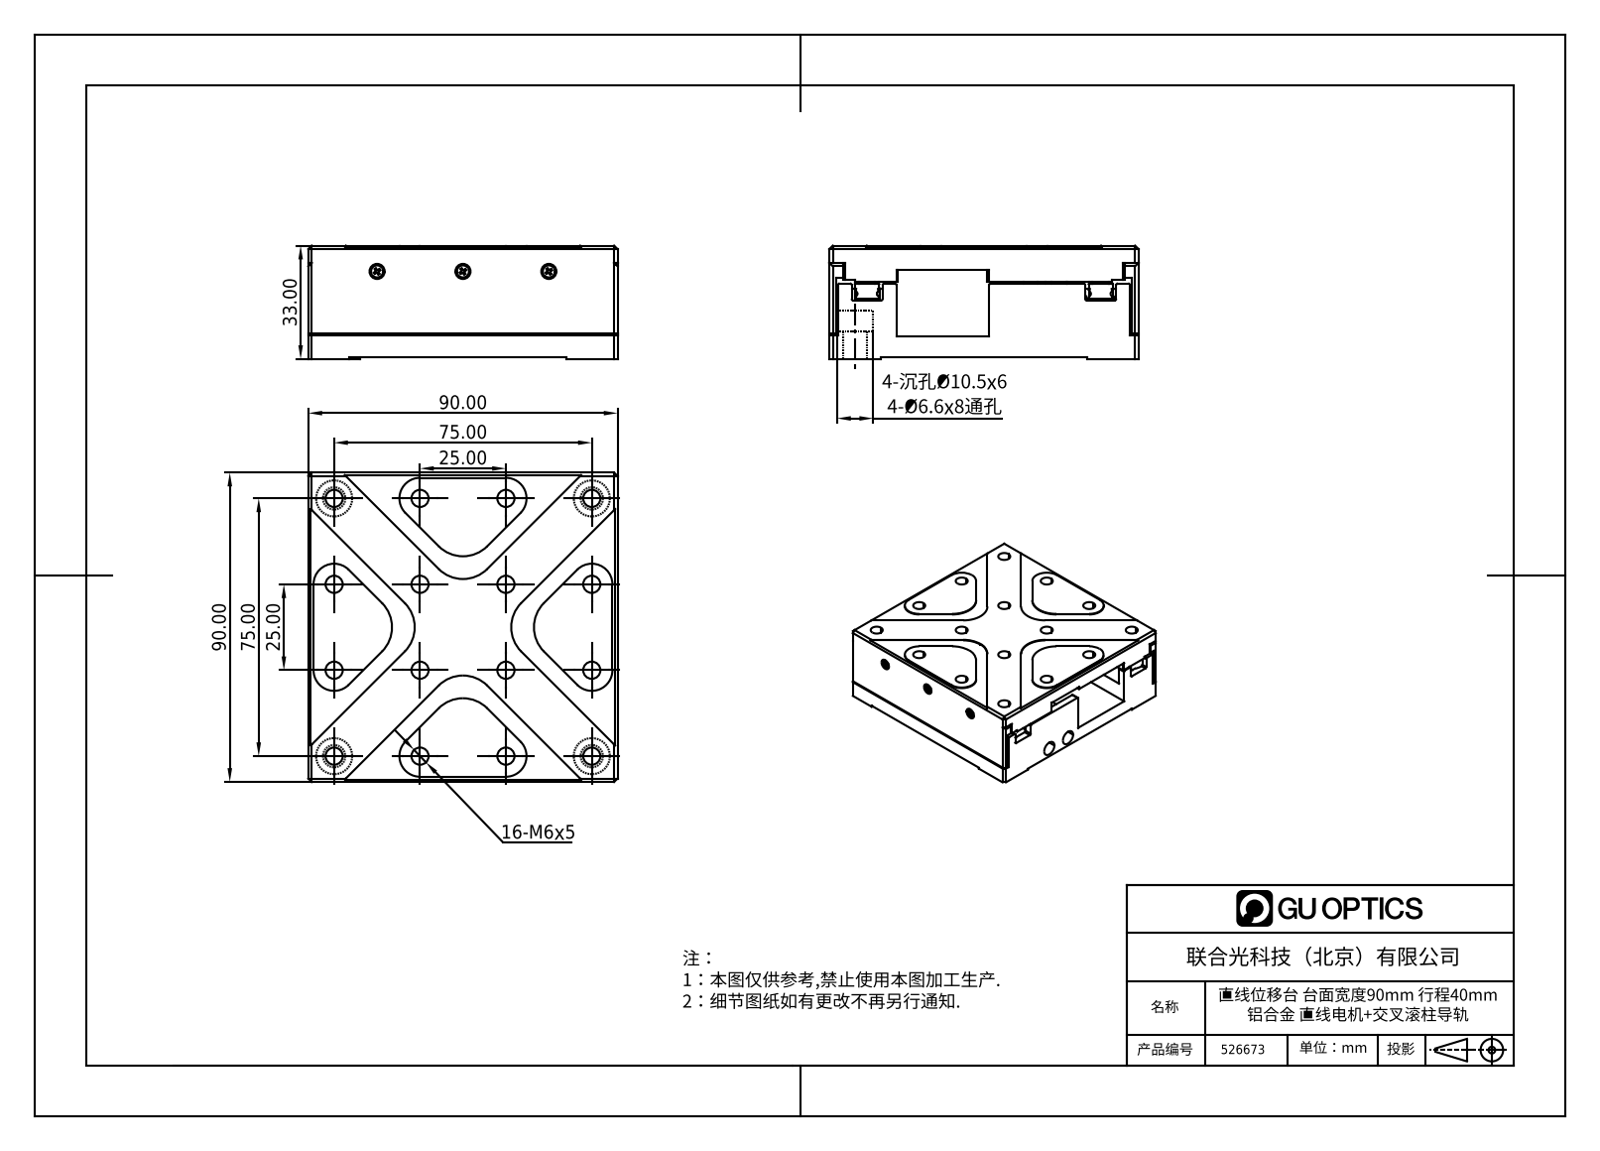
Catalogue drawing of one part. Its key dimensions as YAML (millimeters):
part_name: "FMSS90C-38"
step_written_by: "SolidWorks 2020 (CONFIG_CONTROL_DESIGN)"
units: millimeters
bodies: {solids: 0, faces: 616, planar: 405, cylindrical: 176, other: 35}
overall_size: [90.2, 90, 33]
round_holes:
  - {diameter: 4.4, count: 10}
  - {diameter: 6.5, count: 4}
  - {diameter: 6, count: 2}
  - {diameter: 6.2, count: 2}
round_bosses_or_shafts:
  - {diameter: 5, count: 16}
  - {diameter: 3.5, count: 9}
  - {diameter: 2.5, count: 1}
  - {diameter: 2.3, count: 1}
partial_cylinders:
  - {radius: 0.3, count: 61}
  - {radius: 0.5, count: 20}
  - {radius: 6, count: 8}
  - {radius: 10, count: 8}
  - {radius: 1, count: 4}
  - {radius: 5, count: 4}
  - {radius: 5.25, count: 4}
  - {radius: 2, count: 1}
face_to_face_distances: [6, 7, 32.5, 26.5, 90, 0.5, 19, 1, 15.5, 19.5]
hole_center_spacings: [10, 15.62, 20, 23.32, 12, 30, 32.31, 75]
